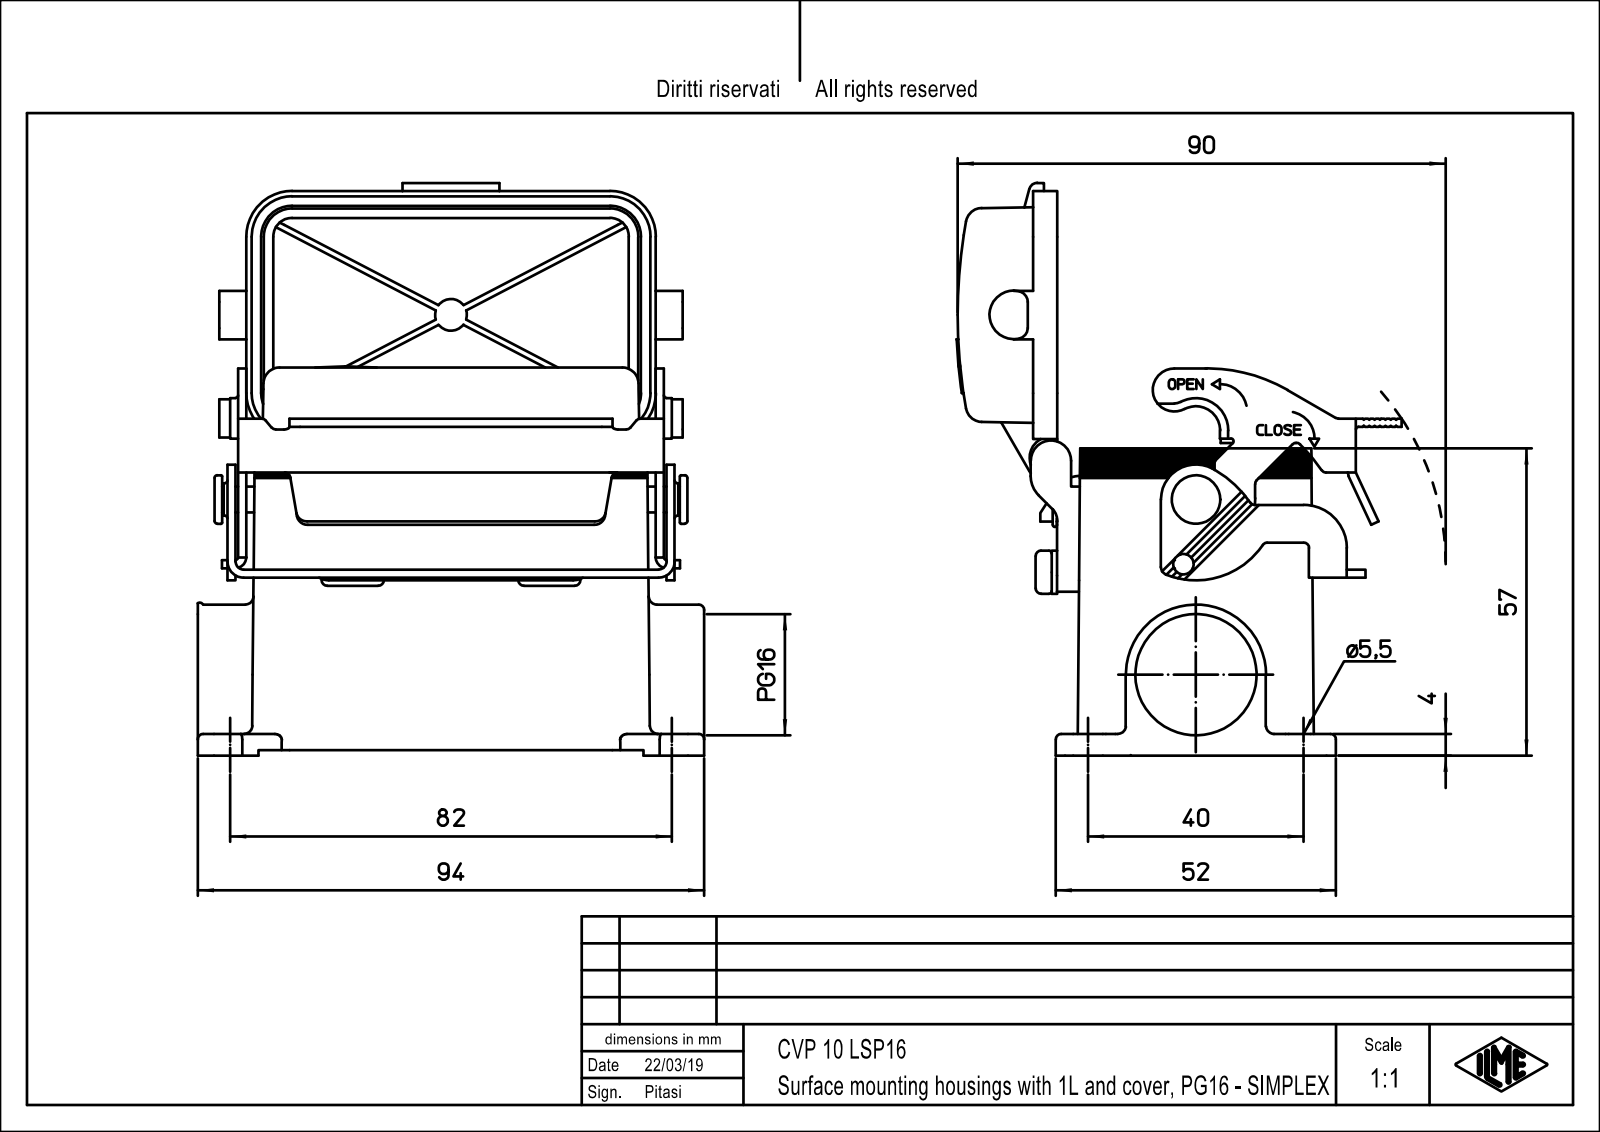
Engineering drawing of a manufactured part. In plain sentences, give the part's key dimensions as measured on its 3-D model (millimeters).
The part is named "CVP_10_LSP16". Its 3-D file was written by "PTC Creo Elements/Direct Modeling 19.0E 27-Jun-2016 (C) Parametric Technology GmbH (AUTOMOTIVE_DESIGN)". It is 1 solid with 609 faces: 385 planar, 202 cylindrical and 22 other. Overall it measures 102.7 by 93.5 by 79.2 millimeters. Its volume is 98 068 cubic millimeters and its surface area 59 749 square millimeters. Round holes: 4 of diameter 2.46, 4 of diameter 3, 4 of diameter 5.5, 1 of diameter 15.16, 1 of diameter 21.16, 1 of diameter 22.5. Round bosses or shafts: 2 of diameter 0.8, 1 of diameter 9, 1 of diameter 8.4, 1 of diameter 8, 1 of diameter 6, 1 of diameter 5. Partial cylindrical surfaces (rounded edges, fillets, slot ends): 20 of radius 2, 15 of radius 3, 8 of radius 1.5, 7 of radius 3.5, 5 of radius 1, 5 of radius 6, 4 of radius 0.5, 4 of radius 1.8. The main face-to-face distances are 4, 40.5, 1.5, 36.5, 2, 44.5, 7.5, 8.25, 3.5, 2.5. The hole center spacings are 14.53, 35.93, 68.81, 76.25, 27, 40, 55.5, 61.72.
